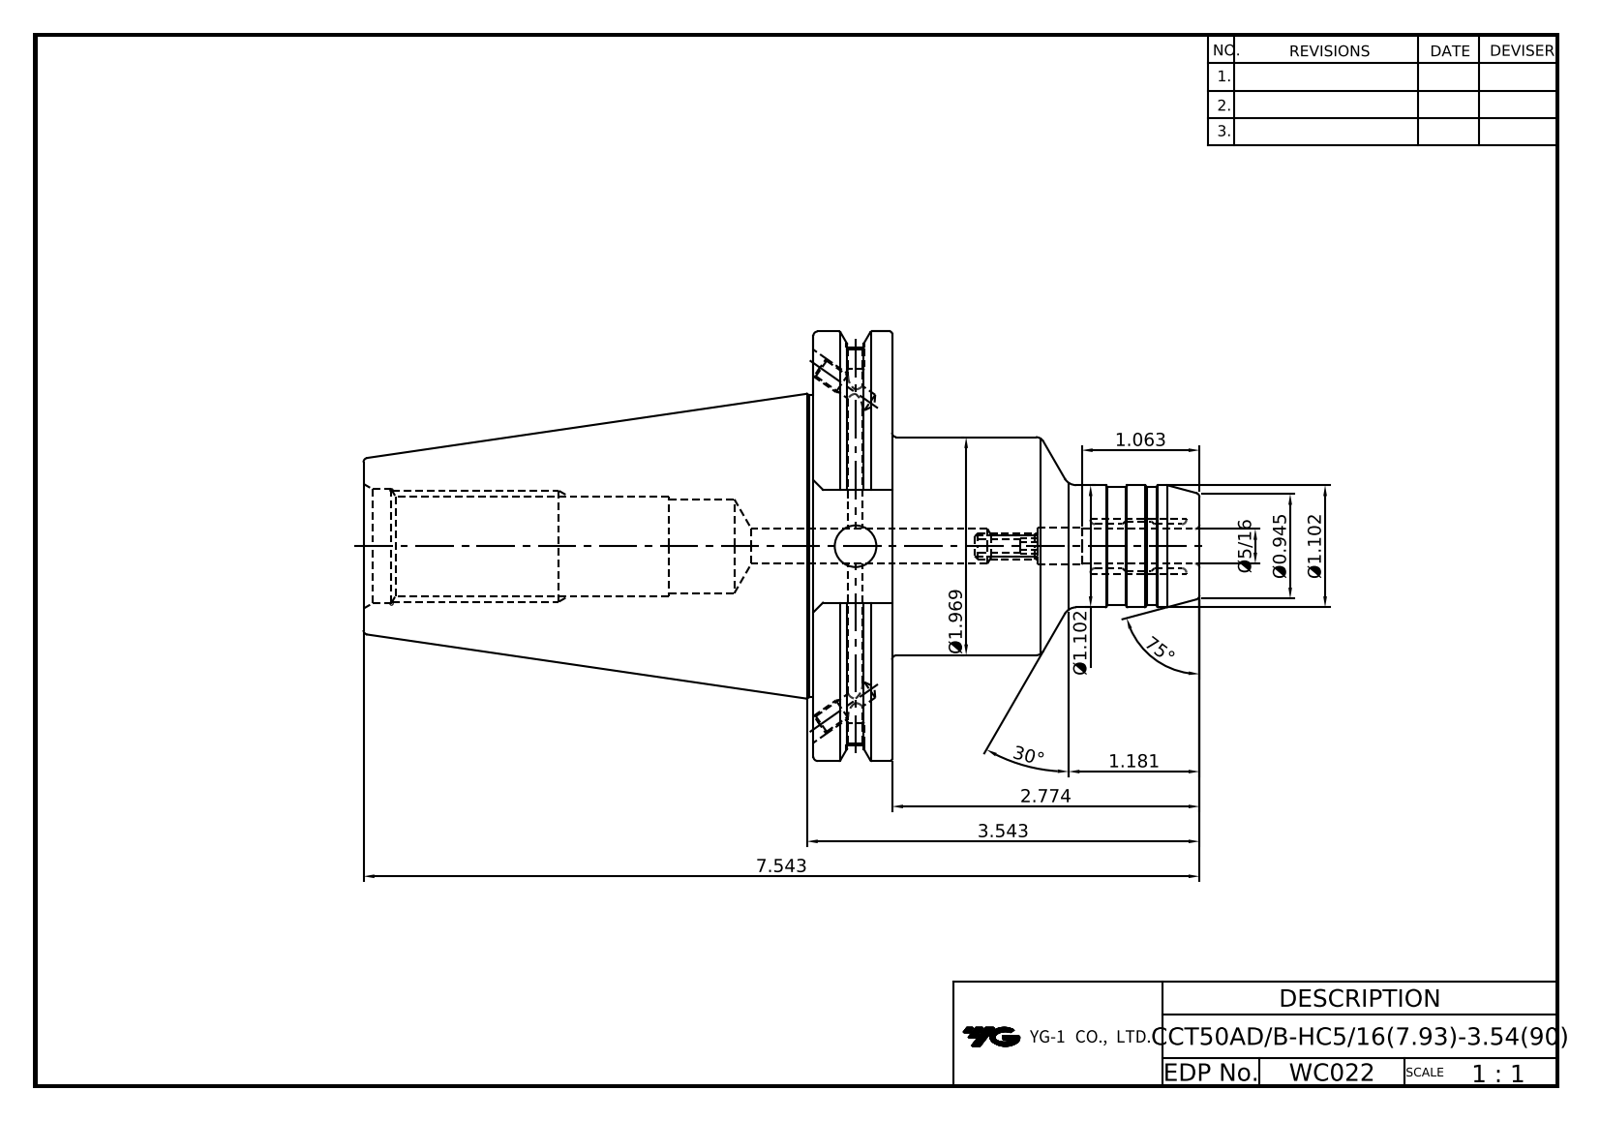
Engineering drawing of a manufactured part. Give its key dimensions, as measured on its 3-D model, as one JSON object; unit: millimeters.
{"part_name": "CCT50ADB-HC7.9375-90", "step_written_by": "Autodesk Inventor 2022 (AUTOMOTIVE_DESIGN)", "units": "millimeters", "bodies": {"solids": 1, "faces": 110, "planar": 38, "cylindrical": 33, "other": 39}, "overall_size": [191.6, 98.42, 94.69], "volume_mm3": 424411, "surface_area_mm2": 53946, "round_holes": [[3.24, 2], [4.13, 2], [4.2, 2], [5, 2], [4.92, 1], [7.94, 1], [8, 1], [9.5, 1], [9.53, 1], [21.5, 1], [21.97, 1], [26.2, 1]], "round_bosses_or_shafts": [[98.42, 1], [91.29, 1], [69.25, 1], [50, 1], [28, 1], [27, 1]], "face_to_face_distances": [17.55, 103.1, 120.65, 73.03, 191.6, 88.5, 70.95, 25.9, 103.5, 0.4]}
